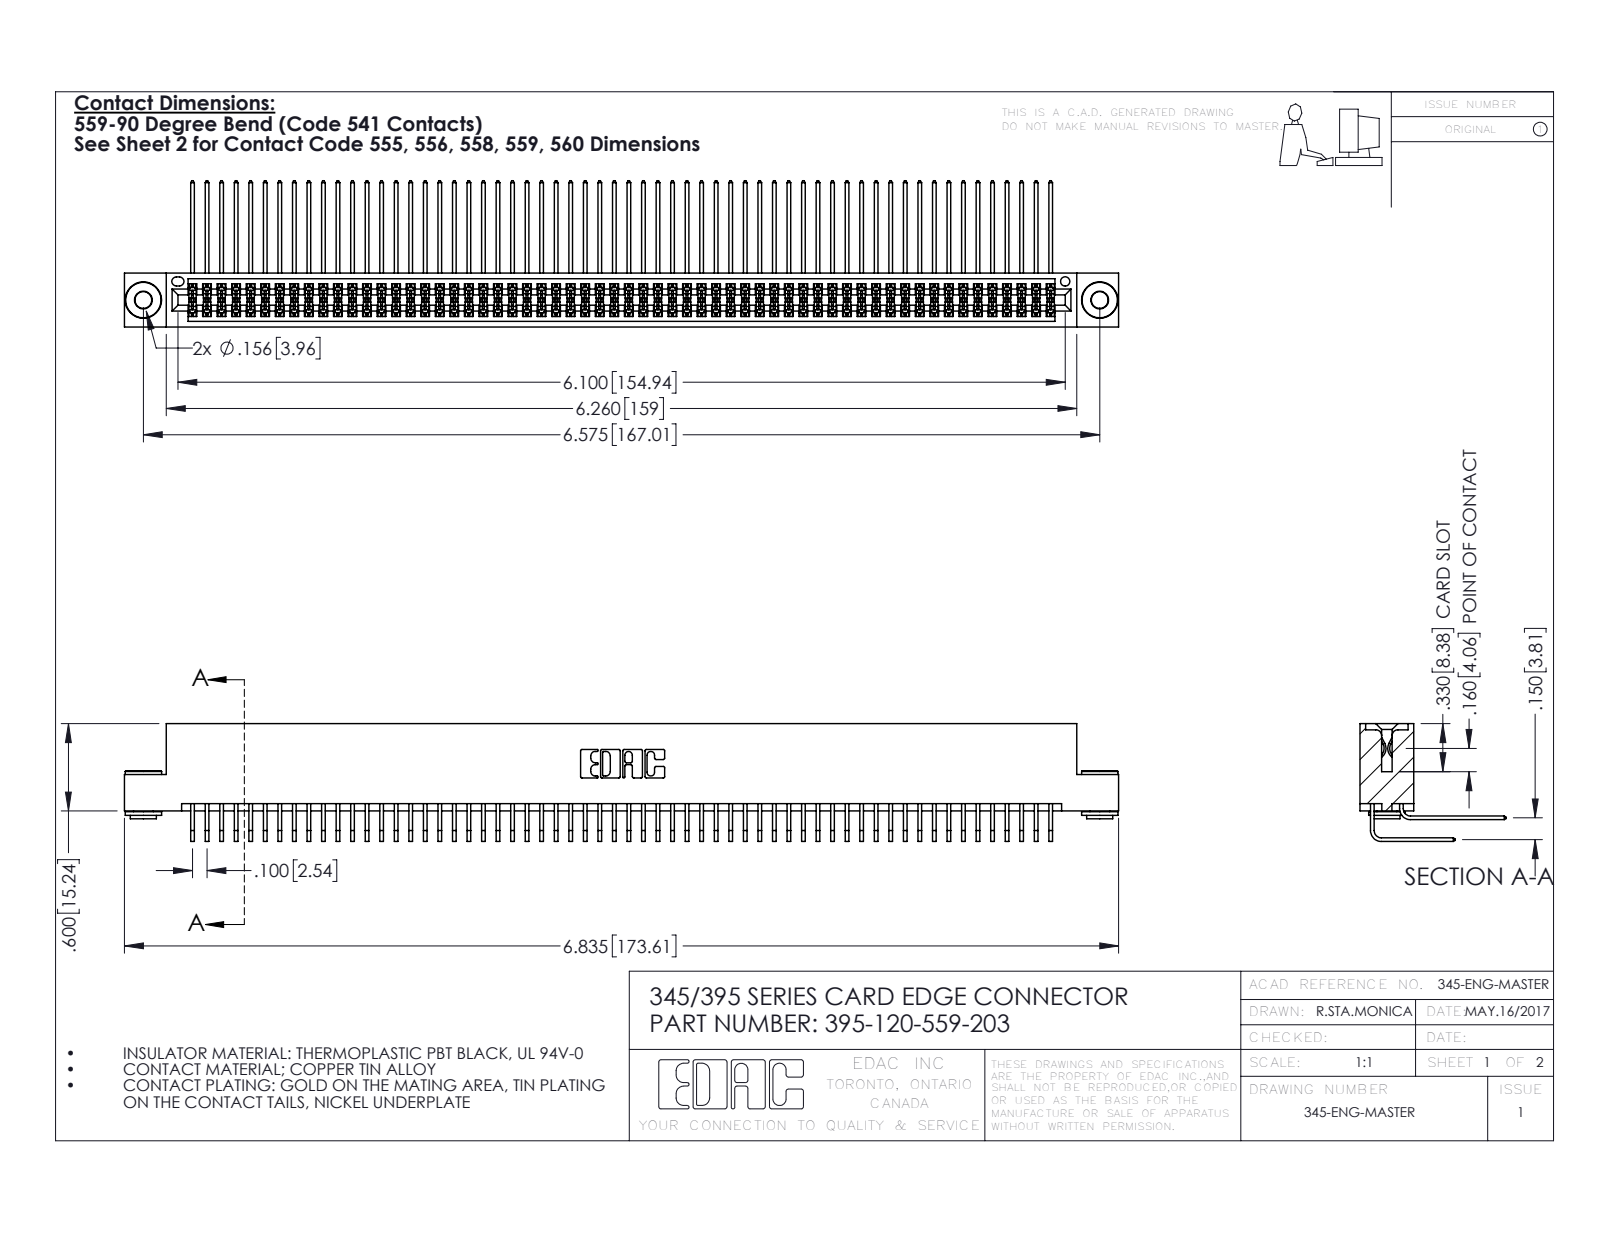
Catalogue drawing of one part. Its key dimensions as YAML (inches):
part_name: "345-250-002_345-250-002-102; 345-292-001_558 559 Tail - 1; 345-292-001_559 Tail - 2; 395-120-559-203 (+1 more)"
step_written_by: "SolidWorks 2016 (CONFIG_CONTROL_DESIGN)"
units: inches
bodies: {solids: 123, faces: 6404, planar: 4290, cylindrical: 2106, other: 8}
overall_size: [6.835, 1.005, 0.809]
volume: 1.083
surface_area: 46.56
round_holes:
  - {diameter: 0.116, count: 2}
  - {diameter: 0.156, count: 2}
  - {diameter: 0.064, count: 1}
round_bosses_or_shafts:
  - {diameter: 0.25, count: 2}
  - {diameter: 0.18, count: 2}
  - {diameter: 0.136, count: 2}
partial_cylinders:
  - {radius: 0.006, count: 181}
  - {radius: 0.01, count: 22}
  - {radius: 0.007, count: 6}
  - {radius: 0.031, count: 6}
  - {radius: 0.026, count: 3}
  - {radius: 0.014, count: 2}
  - {radius: 0.019, count: 2}
  - {radius: 0.022, count: 2}
face_to_face_distances: [0.072, 0.298, 0.2, 0.37, 0.025, 0.098, 0.272, 0.225, 0.175, 0.15]
hole_center_spacings: [0.27, 6.339, 6.575]
